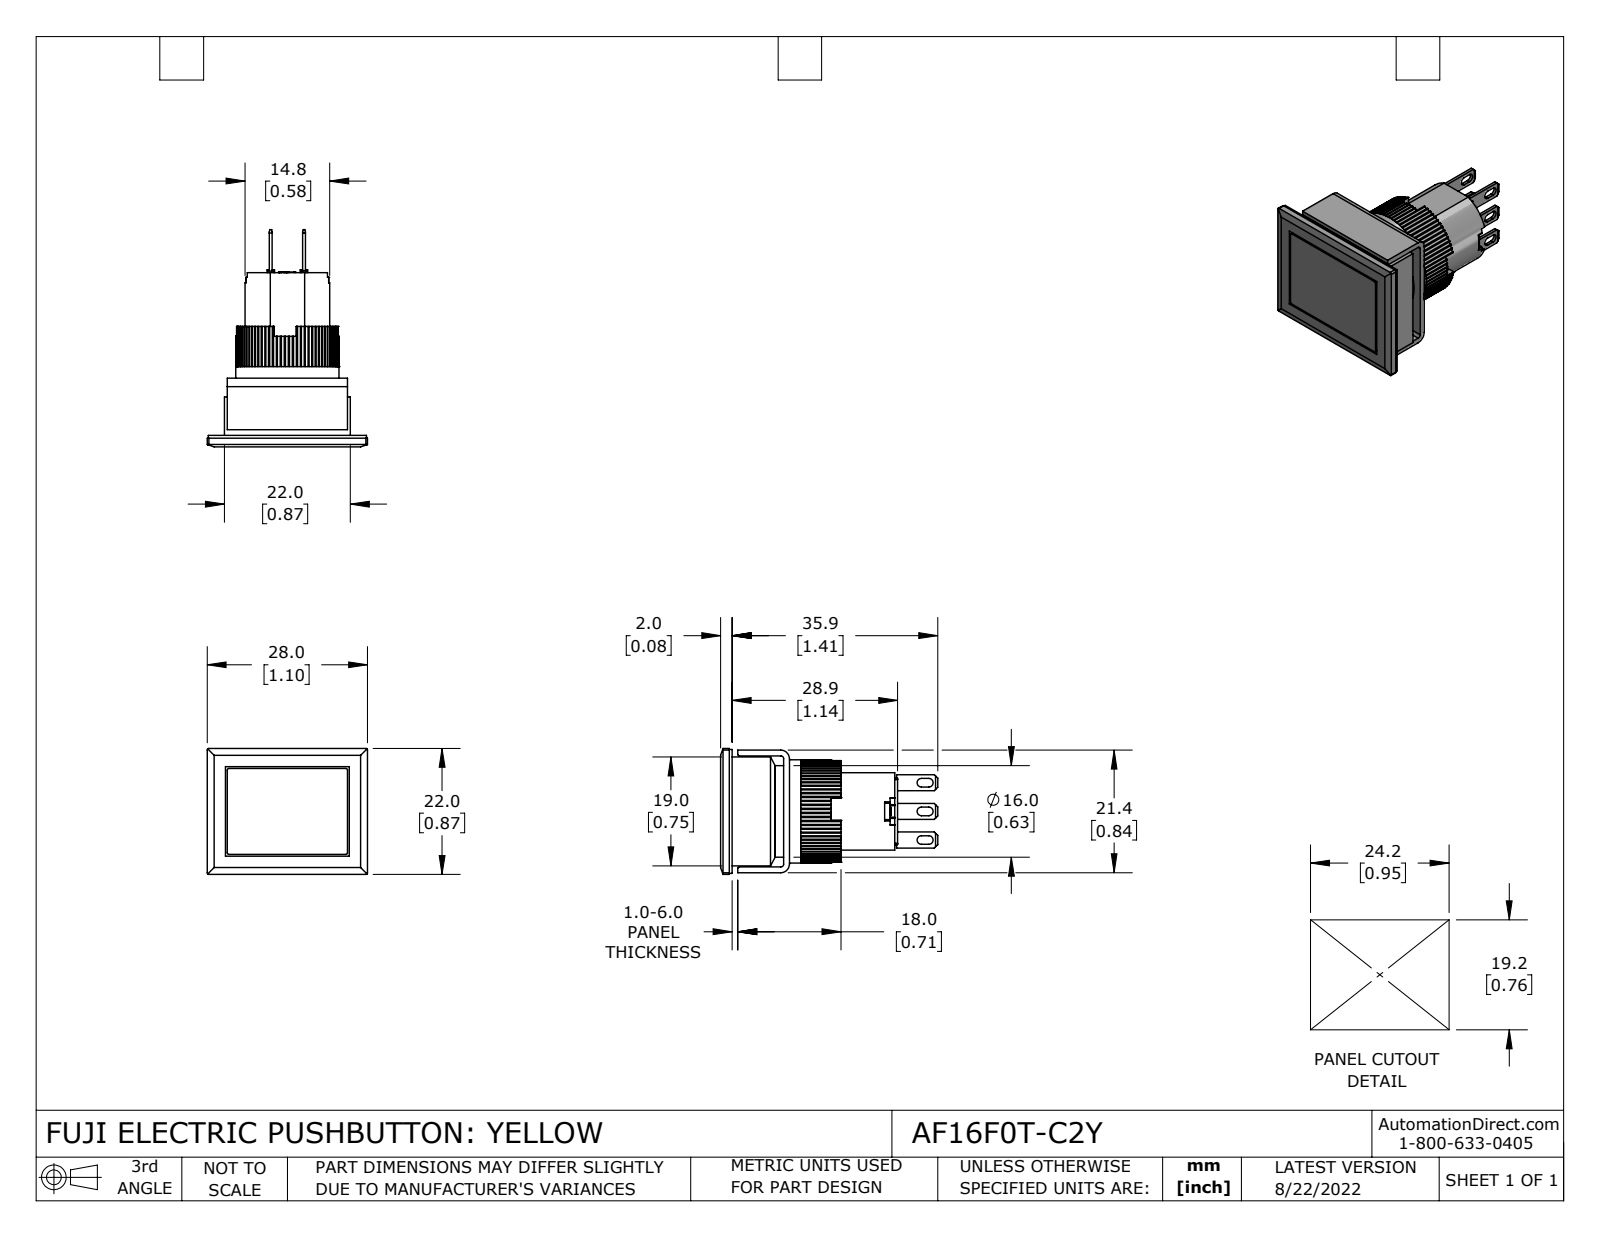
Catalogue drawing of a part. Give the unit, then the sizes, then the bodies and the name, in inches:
Units: inches
Overall size (bounding box): 1.492 × 1.102 × 0.866
Round holes (diameter × count): ⌀0.039 ×1, ⌀0.709 ×1
Round bosses / shafts (diameter × count): ⌀0.63 ×1, ⌀0.583 ×1
Partial cylindrical surfaces — rounded edges, fillets, slot ends (radius × count): R0.01 ×80, R0.008 ×12, R0.012 ×8, R0.03 ×6, R0.02 ×2, R0.059 ×2
Main face-to-face distances: 0.374, 0.059, 0.02, 0.142, 0.039, 0.315, 0.232, 0.083, 0.079, 0.756
Volume: 0.541 in³ · Surface area: 11.85 in²
Bodies: 12 solids, 798 faces (620 planar, 176 cylindrical, 2 other)
Part name (STEP PRODUCT): AF16F0T-C2Y
STEP written by: SolidWorks 2021 (CONFIG_CONTROL_DESIGN)
